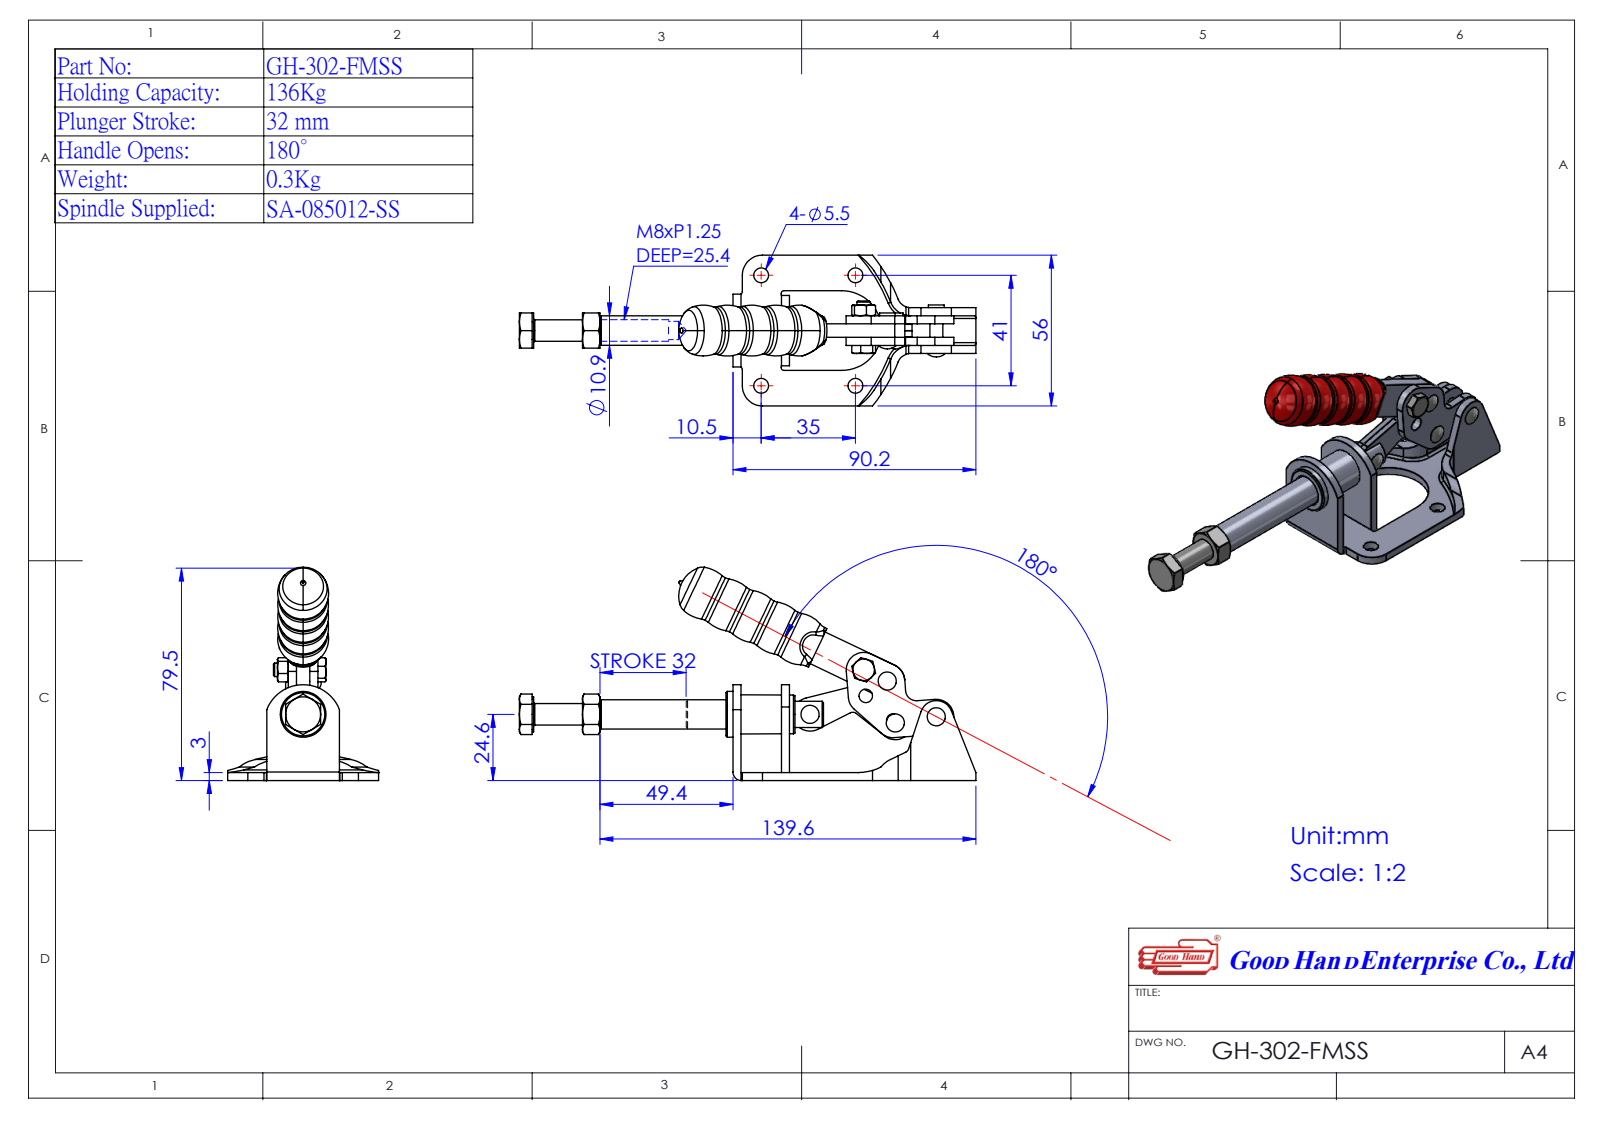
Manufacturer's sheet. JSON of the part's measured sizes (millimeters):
{"part_name": "Group1^GH-302-FMSS; GH-302-FMSS; 1302FSS13; Group4^GH-302-FMSS (+1 more)", "step_written_by": "SolidWorks 2016 (AUTOMOTIVE_DESIGN)", "units": "millimeters", "bodies": {"solids": 5, "faces": 686, "planar": 313, "cylindrical": 125, "other": 248}, "overall_size": [169.7, 79.04, 56], "volume_mm3": 50036, "surface_area_mm2": 28262, "round_holes": [[5.5, 4], [3, 3], [1.91, 1], [10.9, 1], [14.4, 1], [14.6, 1]], "round_bosses_or_shafts": [[5.8, 5], [17, 1], [15.86, 1], [13, 1], [8, 1], [4.8, 1], [1.83, 1]], "partial_cylinders_radius": [[6.5, 6], [0.73, 3], [0.77, 3], [3, 3], [7, 2], [8, 2], [11, 2], [62, 2]], "face_to_face_distances": [3, 11, 8, 3.2, 7.8, 4.8, 17.4, 6, 14, 6.2], "hole_center_spacings": [35, 41, 53.91, 10.82, 16.1, 24.92, 31.8, 39.05]}
